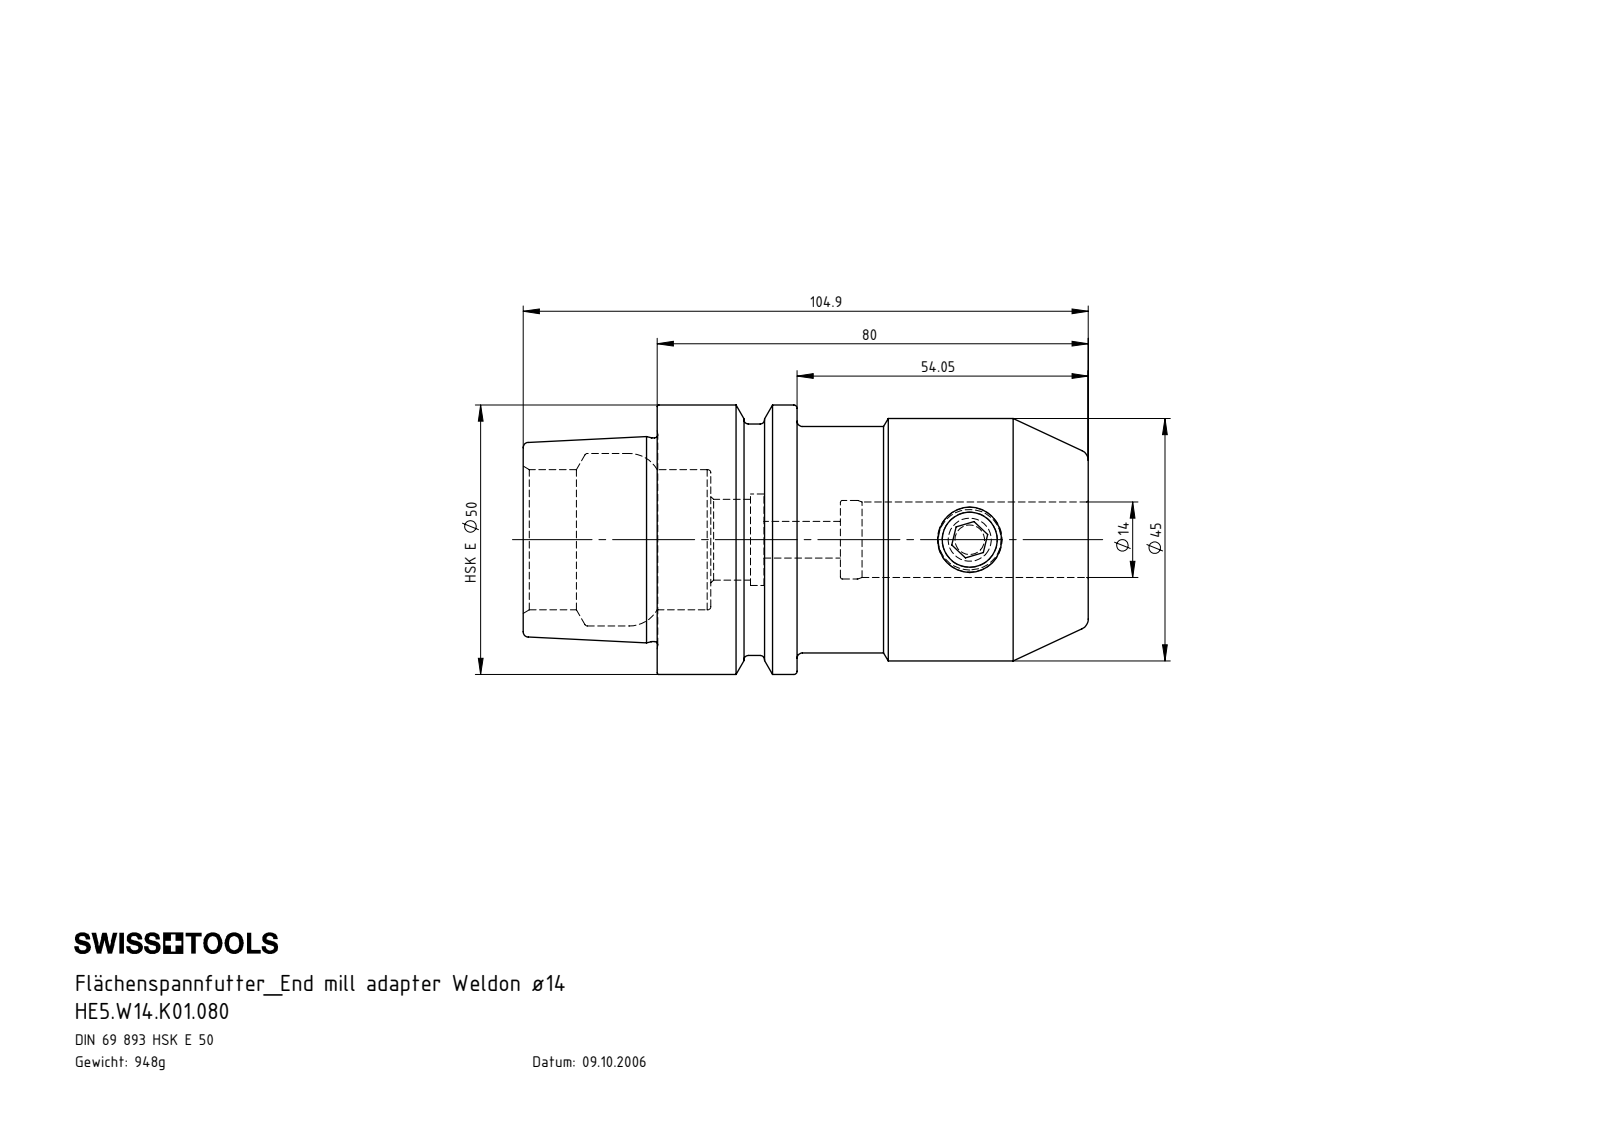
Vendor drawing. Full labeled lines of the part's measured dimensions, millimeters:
Part name (STEP PRODUCT): W12-ER1.001.016; HE5.W14.K01.080; HE5-W14.K01.080_B_Fertigbearbeitung
STEP written by: SolidWorks 2017 (AUTOMOTIVE_DESIGN)
Units: millimetres
Bodies: 2 solids, 113 faces (19 planar, 32 cylindrical, 62 other)
Overall size (bounding box): 104.9 × 50 × 50
Volume: 120 771 mm³ · Surface area: 25 471 mm²
Round holes (diameter × count): ⌀6.8 ×1, ⌀10.25 ×1, ⌀14 ×1, ⌀14.6 ×1, ⌀15 ×1, ⌀17 ×1, ⌀26 ×1, ⌀32 ×1
Round bosses / shafts (diameter × count): ⌀50 ×1, ⌀45 ×1, ⌀42.95 ×1, ⌀42 ×1, ⌀37.81 ×1, ⌀12 ×1
Main face-to-face distances: 80, 25.95, 54.05, 24.9, 50.85, 104.9, 34.85, 9.95, 16, 70.05
